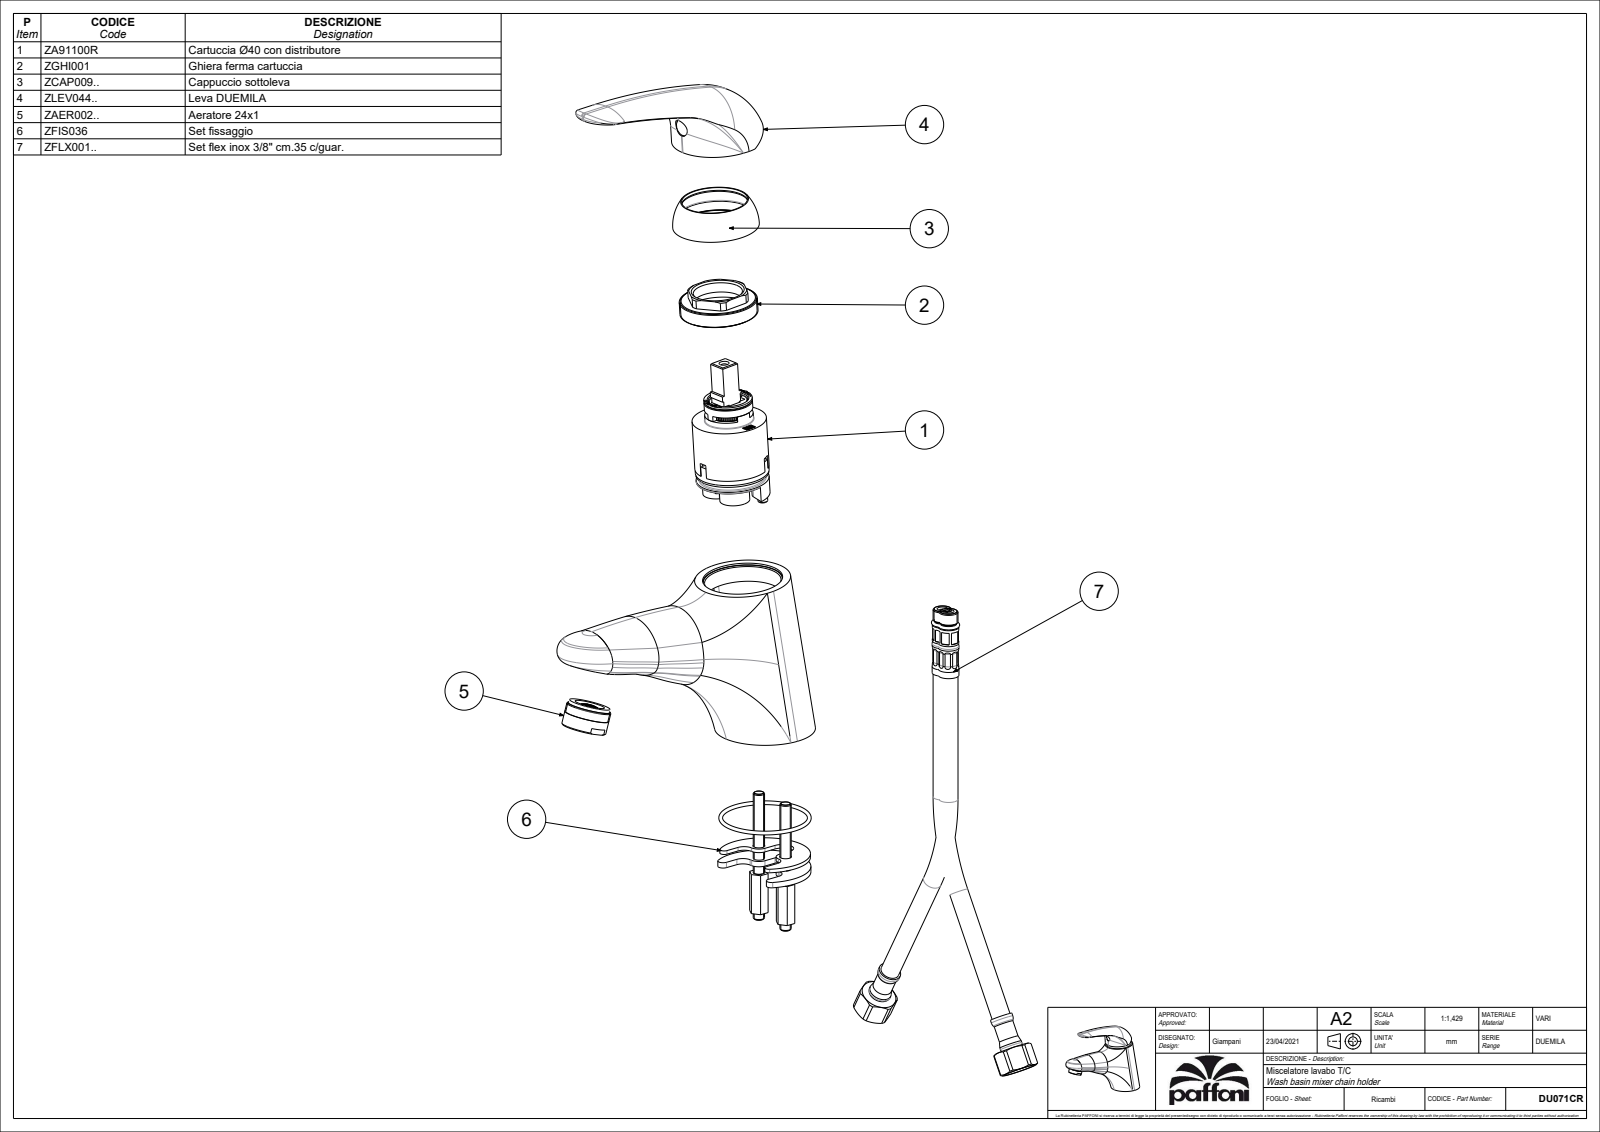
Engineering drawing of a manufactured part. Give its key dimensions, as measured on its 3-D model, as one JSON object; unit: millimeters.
{"part_name": "DU071CR", "step_written_by": "CREO PARAMETRIC BY PTC INC, 2020044 (CONFIG_CONTROL_DESIGN)", "units": "millimeters", "bodies": {"solids": 2, "faces": 2596, "planar": 1945, "cylindrical": 348, "other": 303}, "overall_size": [165.46, 130.21, 53.5], "volume_mm3": 321828, "surface_area_mm2": 82892, "round_holes": [[8, 4], [11, 3], [5.25, 2], [7, 2], [9, 2], [12, 2], [21, 2], [3.3, 1], [4, 1], [5, 1], [6, 1], [7.8, 1]], "round_bosses_or_shafts": [[15.9, 2], [9.4, 2], [44.5, 1], [39.5, 1], [39.2, 1], [38.8, 1], [34.8, 1], [33, 1]], "partial_cylinders_radius": [[0.5, 53], [0.2, 24], [1.5, 6], [0.3, 4], [5.5, 2], [7.5, 2], [15, 2], [24, 2]], "face_to_face_distances": [1, 0.5, 4, 37.41, 5, 1.3, 10, 1.5, 3.5, 50.82], "hole_center_spacings": [9.9, 8.61, 6, 2, 8.6, 10.97, 12.08, 13.04]}
